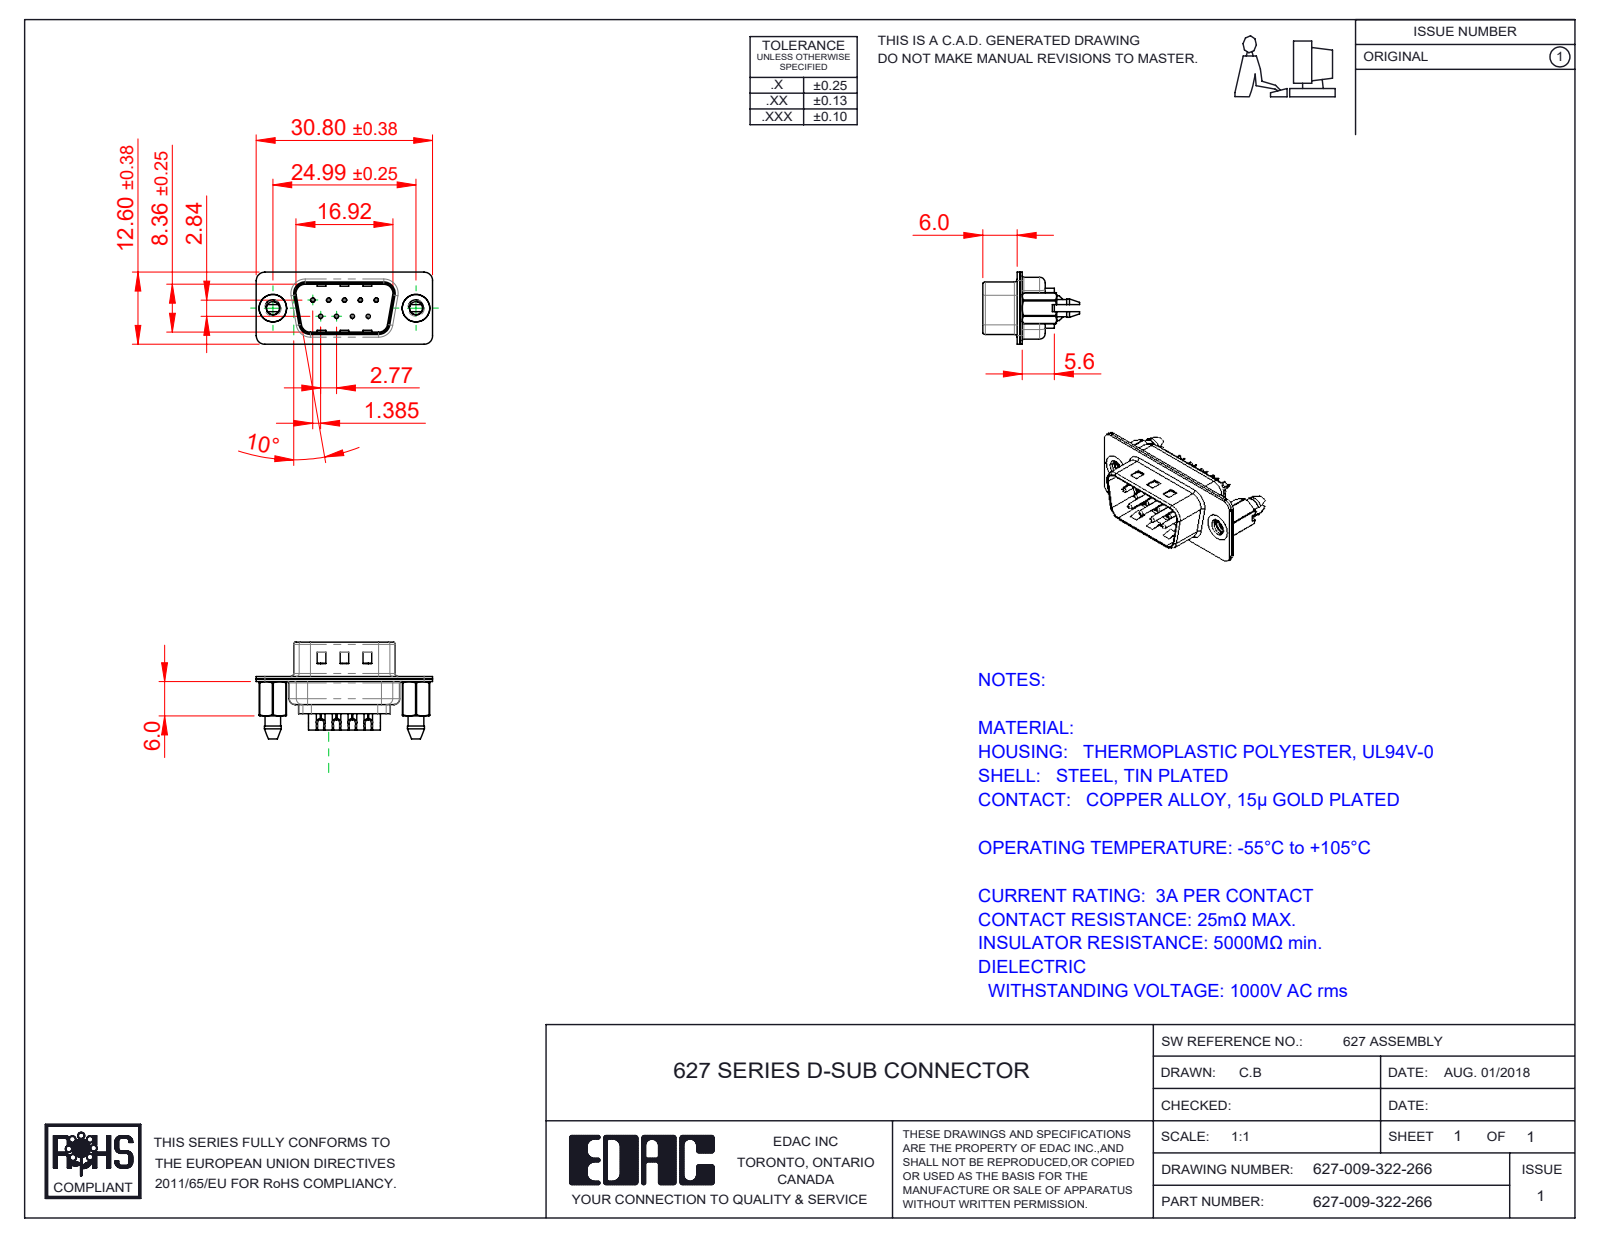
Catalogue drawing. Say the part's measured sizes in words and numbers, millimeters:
The part is named "627 Contact Row 2_22L; 627-009-322-066; 627 4-40 Threaded Boardlock_LP; 627 Shell Front_09 Contacts (+3 more)". Its 3-D file was written by "SolidWorks 2020 (CONFIG_CONTROL_DESIGN)". It is 14 solids with 954 faces: 265 planar, 422 cylindrical and 267 other. Overall it measures 30.8 by 16.9 by 12.6 millimeters. Its volume is 1 430 cubic millimeters and its surface area 4 244 square millimeters. Round holes: 9 of diameter 0.35, 9 of diameter 1.1, 9 of diameter 1.6, 2 of diameter 2.26, 2 of diameter 4, 2 of diameter 4.8. Round bosses or shafts: 9 of diameter 2, 9 of diameter 1.5, 9 of diameter 0.75, 2 of diameter 4.9. Partial cylindrical surfaces (rounded edges, fillets, slot ends): 20 of radius 1.5, 12 of radius 2, 10 of radius 1.6, 8 of radius 0.5, 6 of radius 1, 4 of radius 0.25, 4 of radius 0.6, 4 of radius 0.65. The main face-to-face distances are 0.45, 0.4, 0.9, 0.82, 9.58, 1.4, 8.76, 6.5, 0.5, 1.5. The hole center spacings are 3.16, 2.77, 5.54, 5.03, 5.04, 8.31, 7.48, 7.49.
